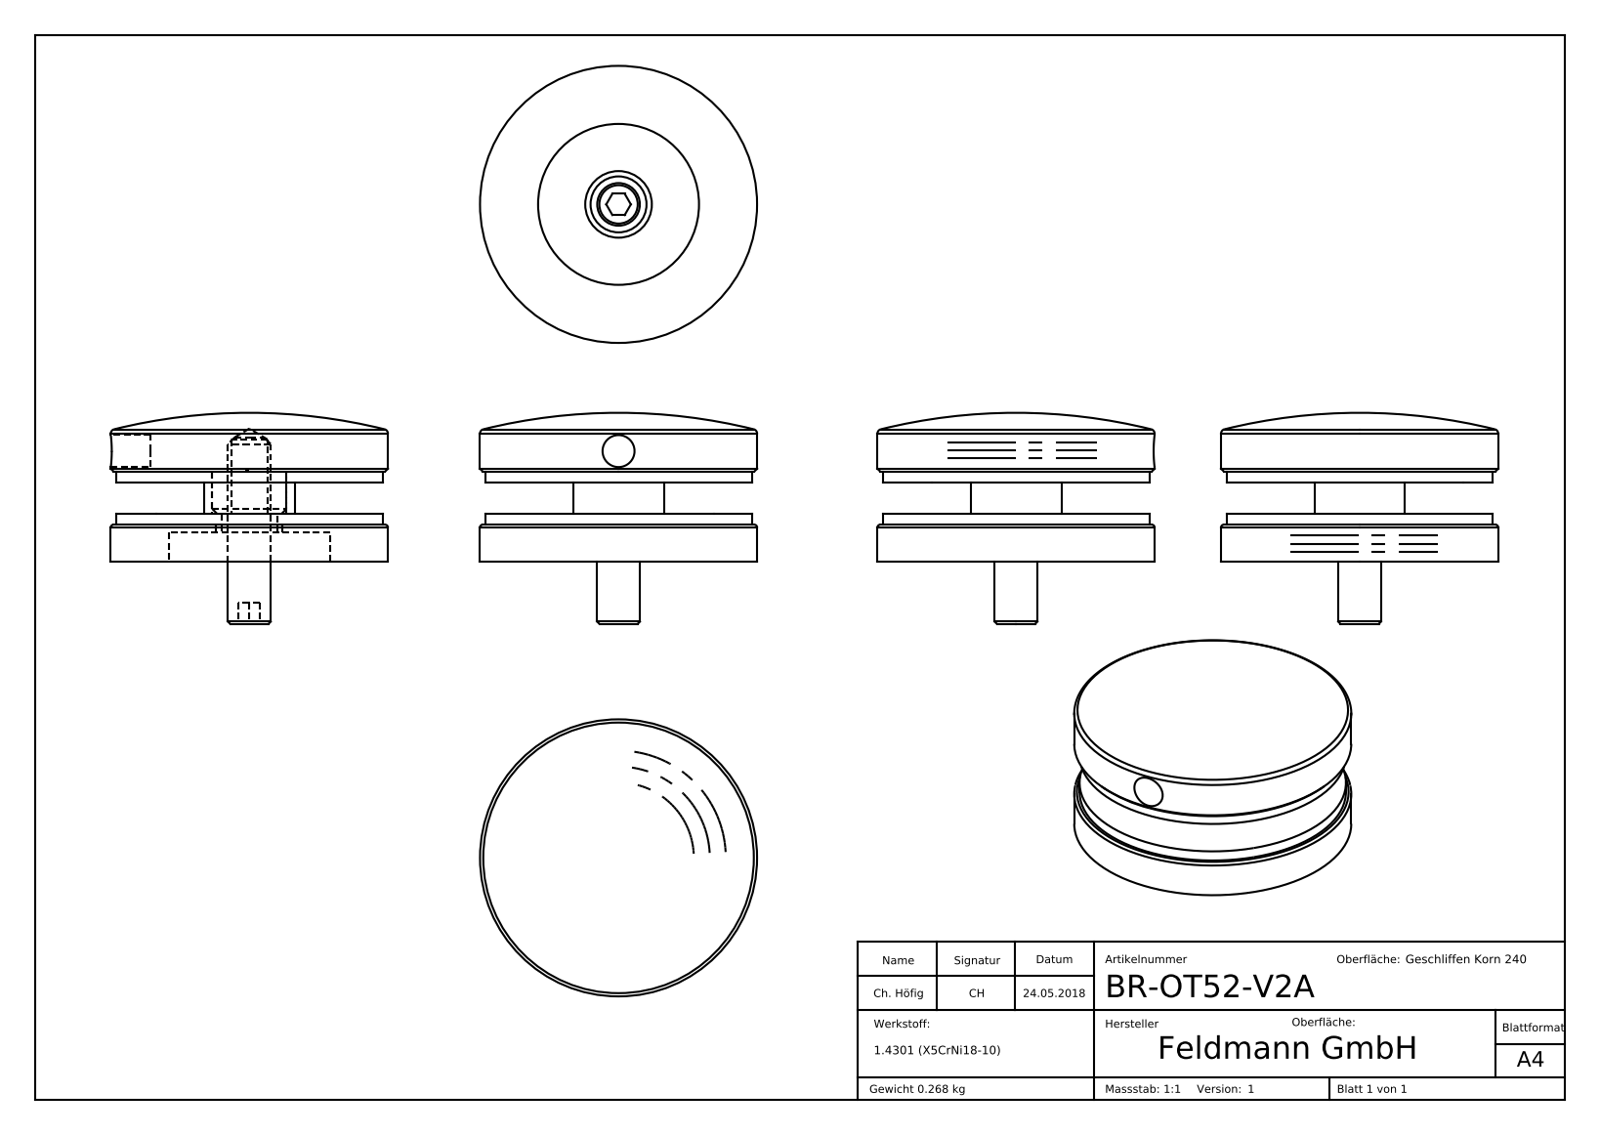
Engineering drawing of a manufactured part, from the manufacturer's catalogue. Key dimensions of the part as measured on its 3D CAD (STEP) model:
Part name (STEP PRODUCT): BR-OT52-XXX Teil2_BR-OT52-XXX Teil2; BR-OT52-XXX Teil1_BR-OT52-V2A Teil1; BR-OT52-V2A; DIN913 M8xXX Konfig_DIN913 M8x35 (+2 more)
STEP written by: SolidWorks 2015 (CONFIG_CONTROL_DESIGN)
Units: millimetres
Bodies: 5 solids, 308 faces (174 planar, 28 cylindrical, 106 other)
Overall size (bounding box): 52 × 52 × 39.61
Volume: 40 646 mm³ · Surface area: 21 792 mm²
Round holes (diameter × count): ⌀6 ×1, ⌀6.8 ×1, ⌀10.5 ×1, ⌀12.5 ×1, ⌀14 ×1, ⌀30.2 ×1
Round bosses / shafts (diameter × count): ⌀52 ×1, ⌀50 ×1, ⌀17 ×1, ⌀8 ×1
Main face-to-face distances: 2, 8, 10, 6, 7, 9, 15, 17, 5.5, 1.5
